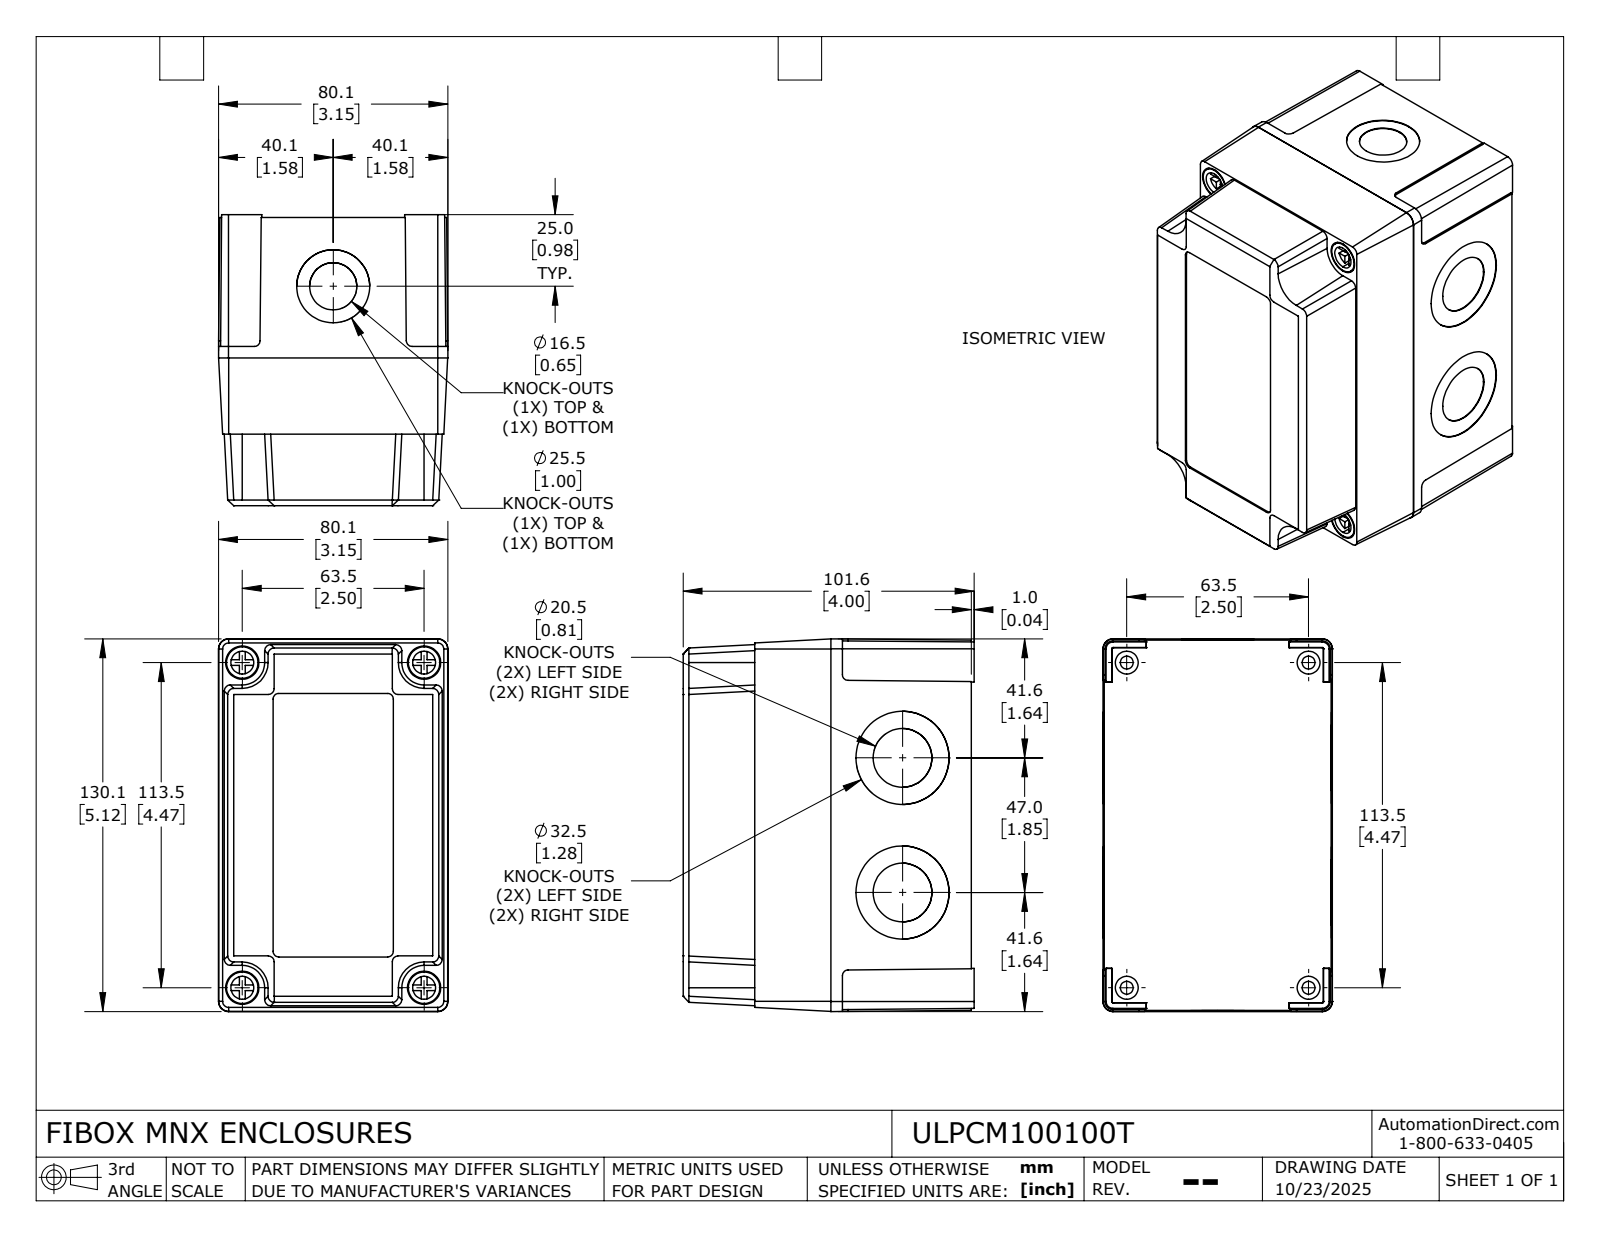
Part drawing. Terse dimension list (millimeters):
name: ULPCM100100T_Default
written by: SolidWorks 2024 (CONFIG_CONTROL_DESIGN)
unit: mm
bodies: 6 solids, 557 faces (327 planar, 184 cylindrical, 46 other)
size: 130.1 × 101.6 × 80.1
volume: 204 300 mm³; area: 131 900 mm²
holes: 8× ⌀3.2, 8× ⌀4, 4× ⌀4.5, 4× ⌀8, 4× ⌀11.6, 4× ⌀20.5, 4× ⌀32.5, 2× ⌀16.5, 2× ⌀25.5
bosses: 8× ⌀8, 8× ⌀2.5, 4× ⌀11, 4× ⌀7.2
rounds: 8× R2, 8× R2.1, 6× R1.4, 4× R0.5, 4× R5, 2× R0.6
face distances: 4.2, 98.3, 3, 95.3, 1.4, 2, 0.6, 0.7, 3.5, 46
hole spacings: 21.4, 22.6, 33.9, 37.5, 49.3, 54.8, 55.2, 57.9
